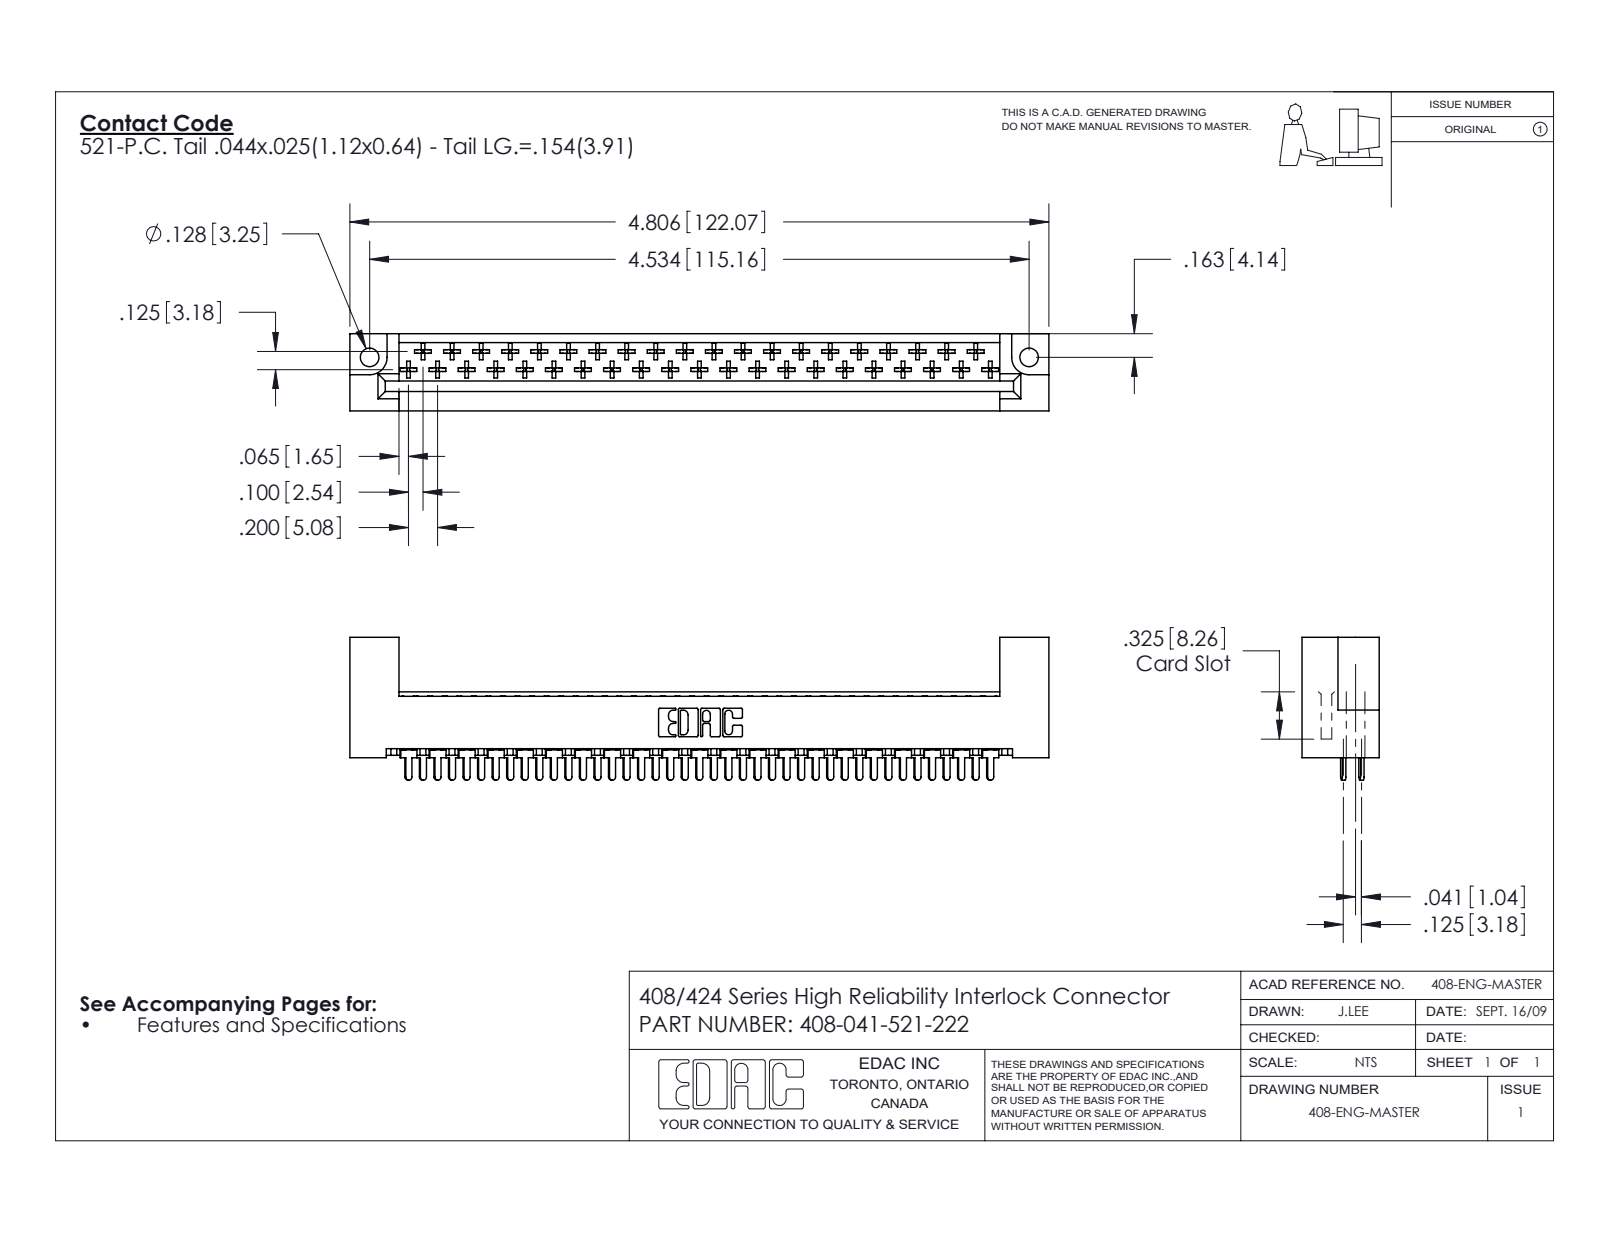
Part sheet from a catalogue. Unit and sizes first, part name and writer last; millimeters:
Units: millimetres
Overall size (bounding box): 122.1 × 24.9 × 13.5
Round holes (diameter × count): ⌀3.3 ×2
Partial cylindrical surfaces — rounded edges, fillets, slot ends (radius × count): R0.3 ×246, R0.5 ×43, R0.6 ×41, R0.3 ×22, R0.2 ×6, R0.8 ×6, R0.7 ×3, R3 ×2
Main face-to-face distances: 13.5, 3.2, 2.5, 0.6, 0.6, 9.2, 6, 6.6, 10.1, 5.5
Hole centre spacings: 115.2
Volume: 15 000 mm³ · Surface area: 17 620 mm²
Bodies: 42 solids, 2394 faces (1811 planar, 419 cylindrical, 164 other)
Part name (STEP PRODUCT): 408-041-521-222; 408-290-001_408-290-121; 408 Part_041 - 2
STEP written by: SolidWorks 2016 (CONFIG_CONTROL_DESIGN)
